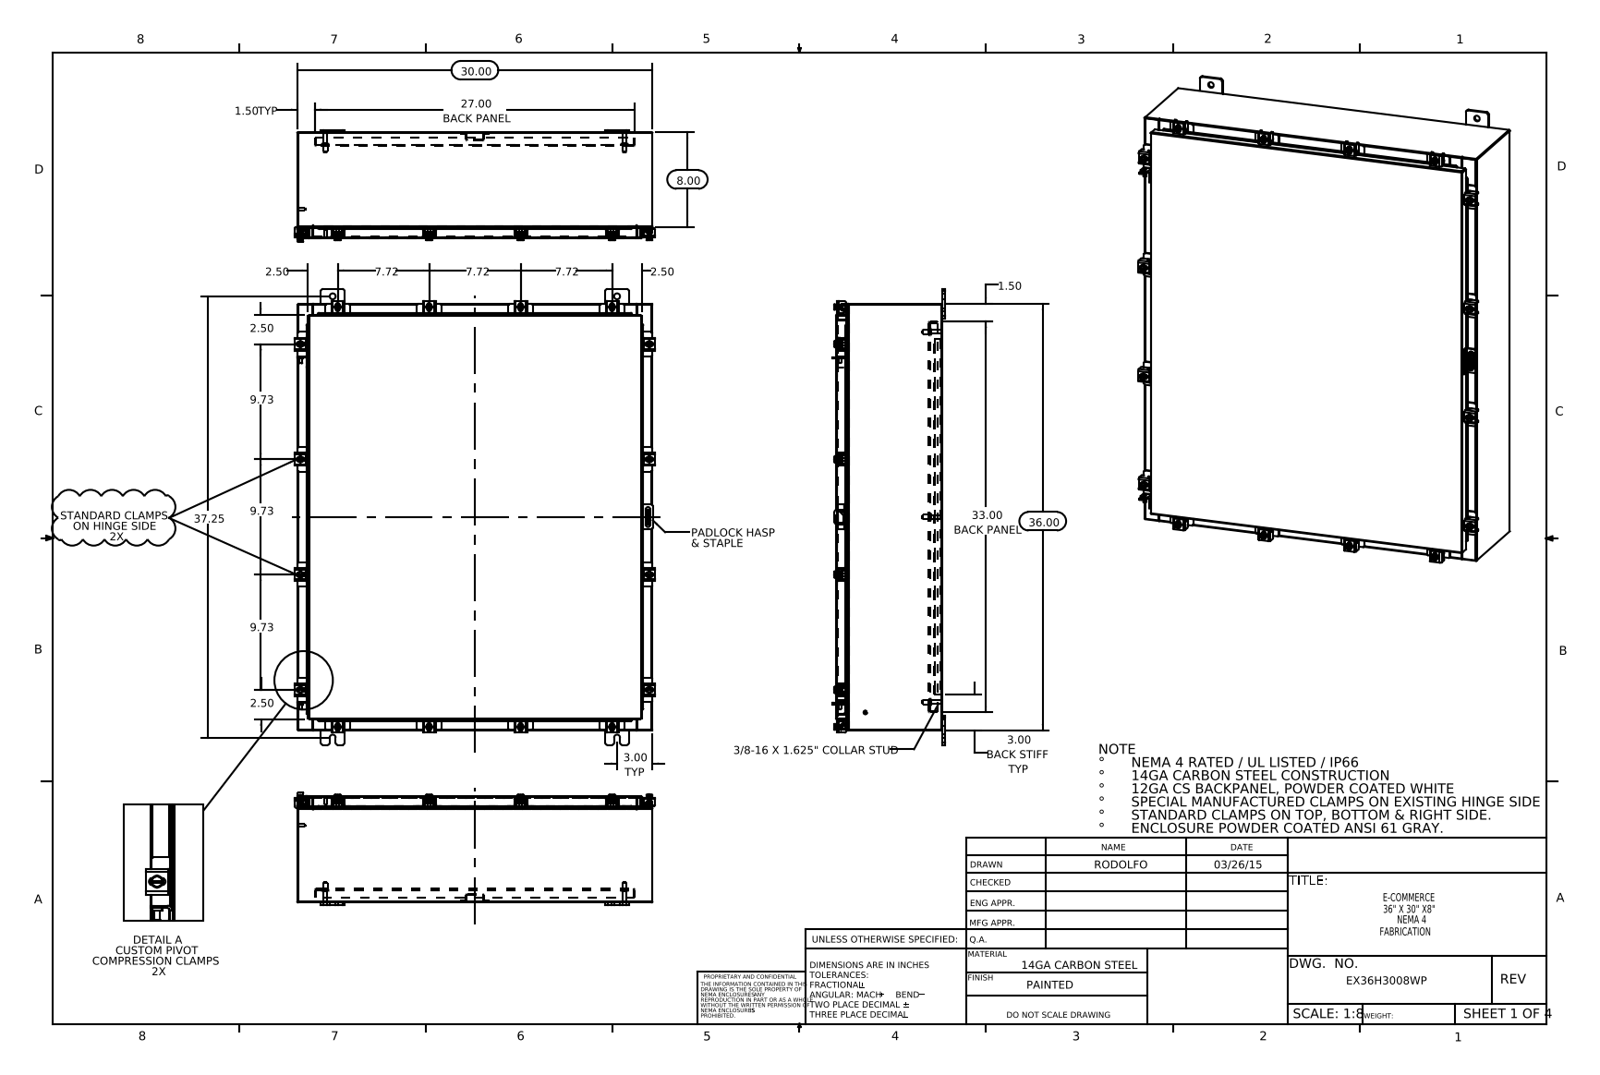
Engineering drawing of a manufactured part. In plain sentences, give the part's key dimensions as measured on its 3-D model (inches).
The part is named "N-WMT04X30402202210-00 22101002; EX36H3008WP Padlock Hasp; 30X10 Clamp Bracket2; EX36H3008WP Padlock Staple (+8 more)". Its 3-D file was written by "SolidWorks 2014 (AUTOMOTIVE_DESIGN)". It is 104 solids with 2594 faces: 1371 planar, 1011 cylindrical and 212 other. Overall it measures 38.5 by 30.421 by 9.453 inches. Its volume is 381.4 cubic inches and its surface area 9 441 square inches. Round holes: 16 of diameter 0.213, 16 of diameter 0.26, 10 of diameter 0.5, 1 of diameter 0.125, 1 of diameter 0.25. Round bosses or shafts: 16 of diameter 0.5, 16 of diameter 0.25, 14 of diameter 0.399, 6 of diameter 0.625, 6 of diameter 0.375, 6 of diameter 0.33, 2 of diameter 0.315, 2 of diameter 0.236. Partial cylindrical surfaces (rounded edges, fillets, slot ends): 70 of radius 0.06, 32 of radius 0.141, 30 of radius 0.013, 30 of radius 0.12, 26 of radius 0.088, 24 of radius 0.19, 22 of radius 0.09, 21 of radius 0.05. The main face-to-face distances are 0.075, 8.9, 8.826, 8.975, 0.104, 1, 1.075, 7.826, 7.9, 1.179. The hole center spacings are 31.017, 2.347, 4.44, 5.299, 9.73, 10.964, 13.241, 14.744.
